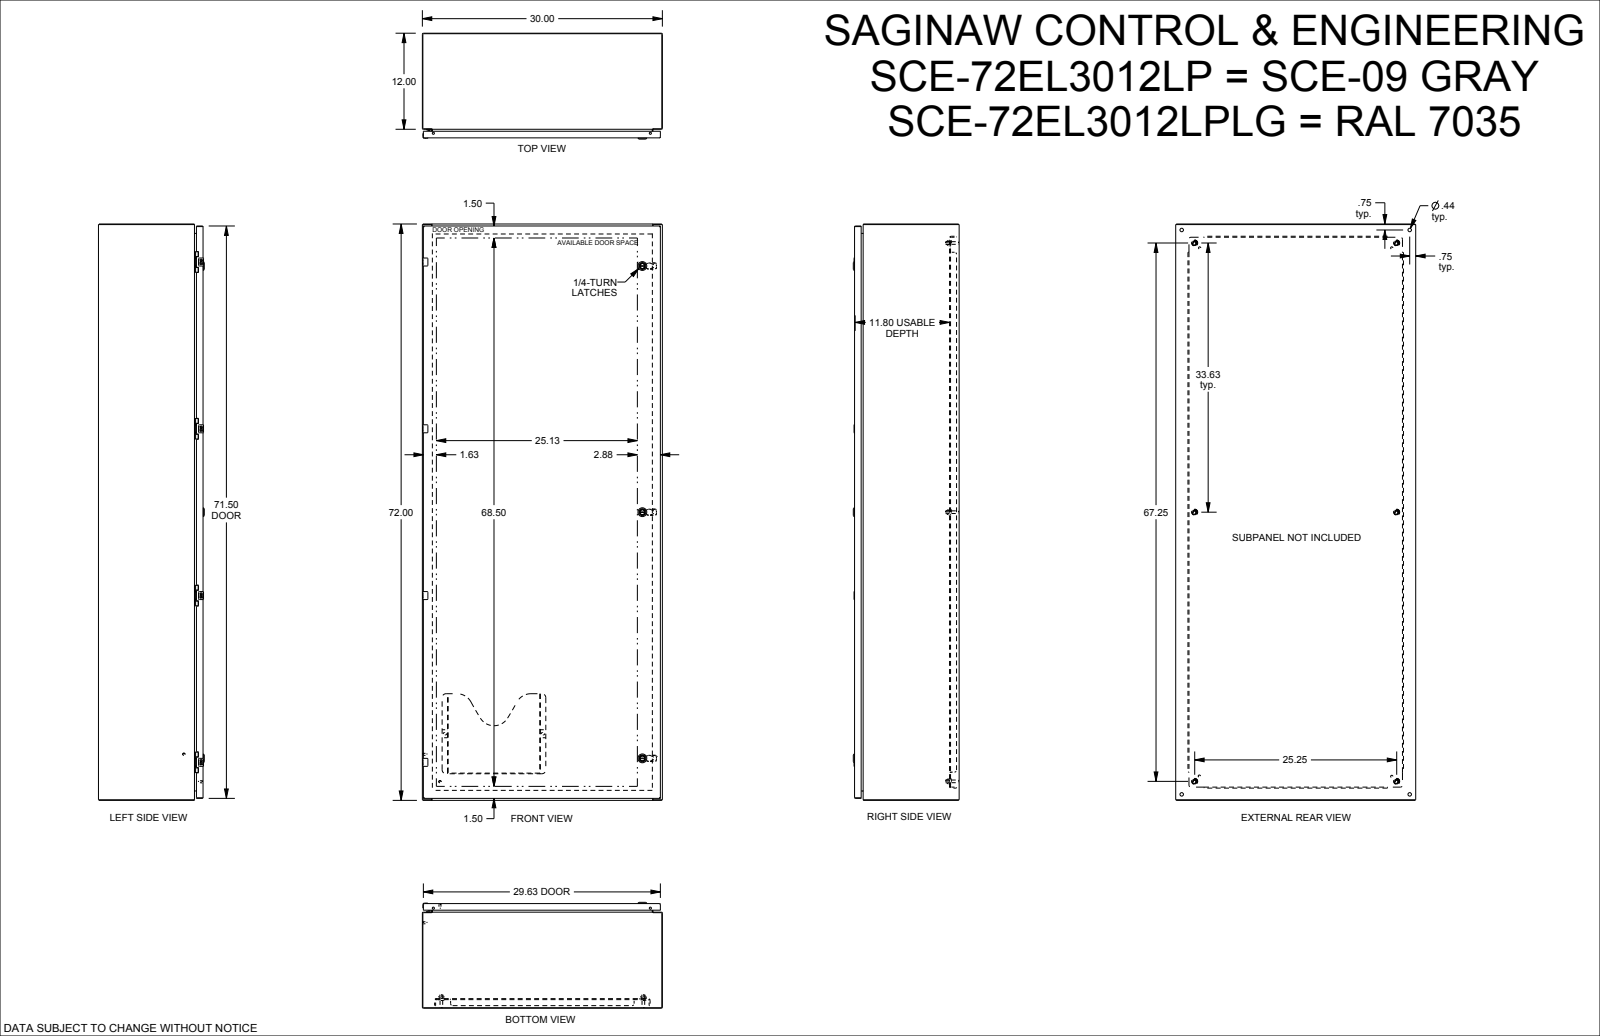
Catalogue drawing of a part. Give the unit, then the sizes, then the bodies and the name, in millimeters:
Units: millimetres
Overall size (bounding box): 1828.8 × 762 × 336
Round holes (diameter × count): ⌀6.8 ×10, ⌀4.4 ×8, ⌀5.2 ×8, ⌀6.2 ×8, ⌀9.5 ×8, ⌀9.3 ×6, ⌀12.7 ×6, ⌀1 ×4, ⌀4 ×4, ⌀5.5 ×4, ⌀7.1 ×4, ⌀11.1 ×4
Round bosses / shafts (diameter × count): ⌀4.3 ×12, ⌀6.4 ×8, ⌀6.1 ×8, ⌀9.3 ×6, ⌀8.4 ×6, ⌀5 ×5, ⌀6.3 ×4, ⌀28 ×3
Partial cylindrical surfaces — rounded edges, fillets, slot ends (radius × count): R0.3 ×82, R0.3 ×40, R0.4 ×40, R0.5 ×28, R0.6 ×20, R2.5 ×20, R0.8 ×19, R0.8 ×18
Main face-to-face distances: 1.9, 1.9, 328.2, 330.1, 332.1, 330.1, 3.2, 30.5, 301.6, 25.4
Hole centre spacings: 529.2, 25, 1058.3, 0.5, 12.5, 529.2, 12.5, 504.2
Bodies: 0 solids, 4253 faces (2029 planar, 1206 cylindrical, 1018 other)
Part name (STEP PRODUCT): SCE-72EL3012LPLG
STEP written by: SolidWorks 2019 (CONFIG_CONTROL_DESIGN)
